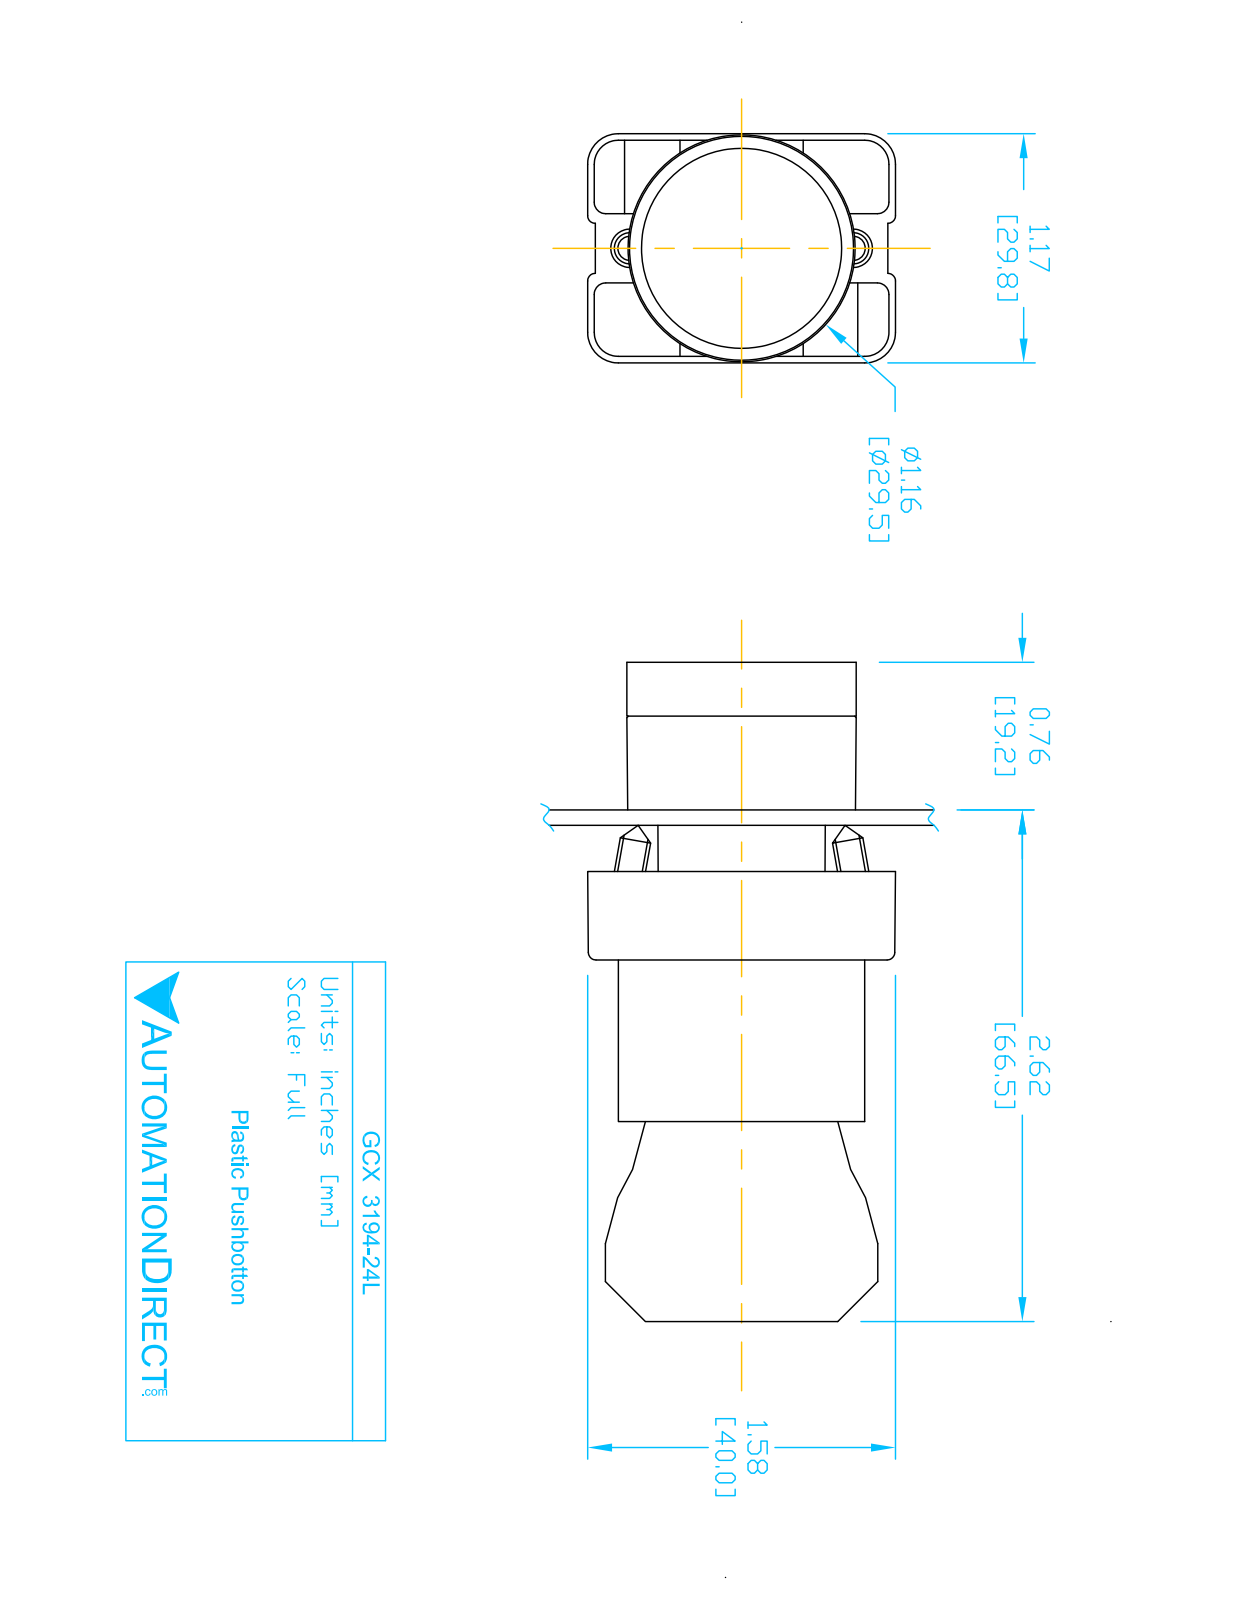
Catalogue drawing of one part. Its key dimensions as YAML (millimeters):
part_name: "GCX3194L OPERATOR; ECX1050; CONTACT BLOCK; GCX3194-24L (+1 more)"
step_written_by: "SolidWorks 2016 (AUTOMOTIVE_DESIGN)"
units: millimeters
bodies: {solids: 8, faces: 431, planar: 252, cylindrical: 148, other: 31}
overall_size: [84.3, 40.2, 29.9]
volume: 45790
surface_area: 25010
round_holes:
  - {diameter: 2, count: 2}
  - {diameter: 3.1, count: 2}
  - {diameter: 3.3, count: 2}
  - {diameter: 2.2, count: 1}
  - {diameter: 5, count: 1}
  - {diameter: 11.9, count: 1}
  - {diameter: 22.3, count: 1}
  - {diameter: 22.6, count: 1}
  - {diameter: 26, count: 1}
round_bosses_or_shafts:
  - {diameter: 4, count: 4}
  - {diameter: 29.8, count: 1}
  - {diameter: 25.5, count: 1}
  - {diameter: 24, count: 1}
  - {diameter: 21.7, count: 1}
  - {diameter: 19.8, count: 1}
  - {diameter: 12.8, count: 1}
partial_cylinders:
  - {radius: 1.5, count: 24}
  - {radius: 1, count: 12}
  - {radius: 3.1, count: 12}
  - {radius: 4, count: 12}
  - {radius: 1, count: 8}
  - {radius: 3.3, count: 2}
  - {radius: 0.5, count: 1}
  - {radius: 1.6, count: 1}
face_to_face_distances: [21, 14.7, 51.3, 30.3, 29.7, 7, 58.3, 37.3, 0.8, 0.8]
hole_center_spacings: [6, 13.8, 12, 12.4]
